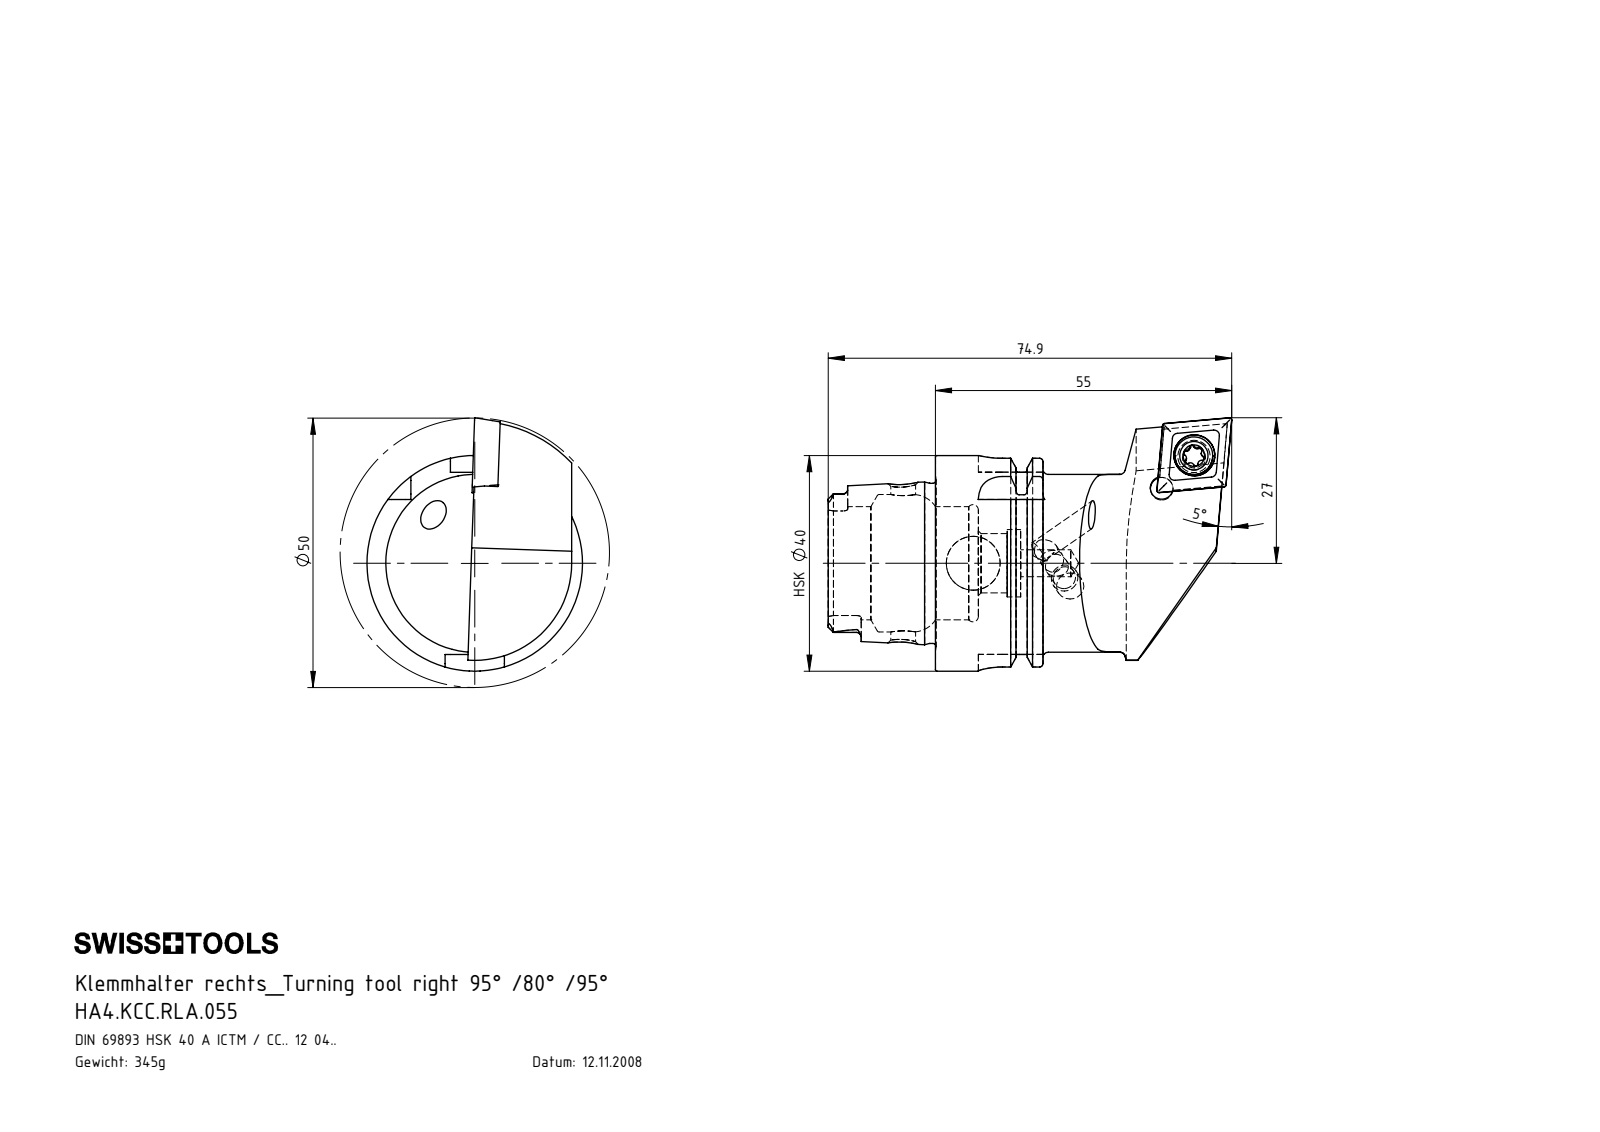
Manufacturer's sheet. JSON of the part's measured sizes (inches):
{"part_name": "HA4-KCC.RLA.055; KVT_MB_600_050; CCMT120404; WCC-ER2.001.010_A (+1 more)", "step_written_by": "SolidWorks 2012 (CONFIG_CONTROL_DESIGN)", "units": "inches", "bodies": {"solids": 5, "faces": 305, "planar": 75, "cylindrical": 92, "other": 138}, "overall_size": [2.949, 1.85, 1.575], "volume_in3": 2.684, "surface_area_in2": 22.55, "round_holes": [[0.165, 4], [0.197, 2], [0.157, 1], [0.181, 1], [0.217, 1], [0.299, 1], [0.394, 1], [0.433, 1], [0.492, 1], [0.827, 1], [1.004, 1]], "round_bosses_or_shafts": [[0.197, 2], [1.575, 1], [1.368, 1], [1.299, 1], [1.17, 1], [0.276, 1]], "partial_cylinders_radius": [[0.015, 6], [0.035, 6], [0.177, 4], [0.027, 3], [0.027, 3], [0.072, 2], [0.074, 2], [0.157, 1]], "face_to_face_distances": [0.313, 0.785, 0.472, 0.783, 1.096, 1.569, 0.175, 1.406, 0.622, 0.309], "hole_center_spacings": [0.333, 0.338]}
